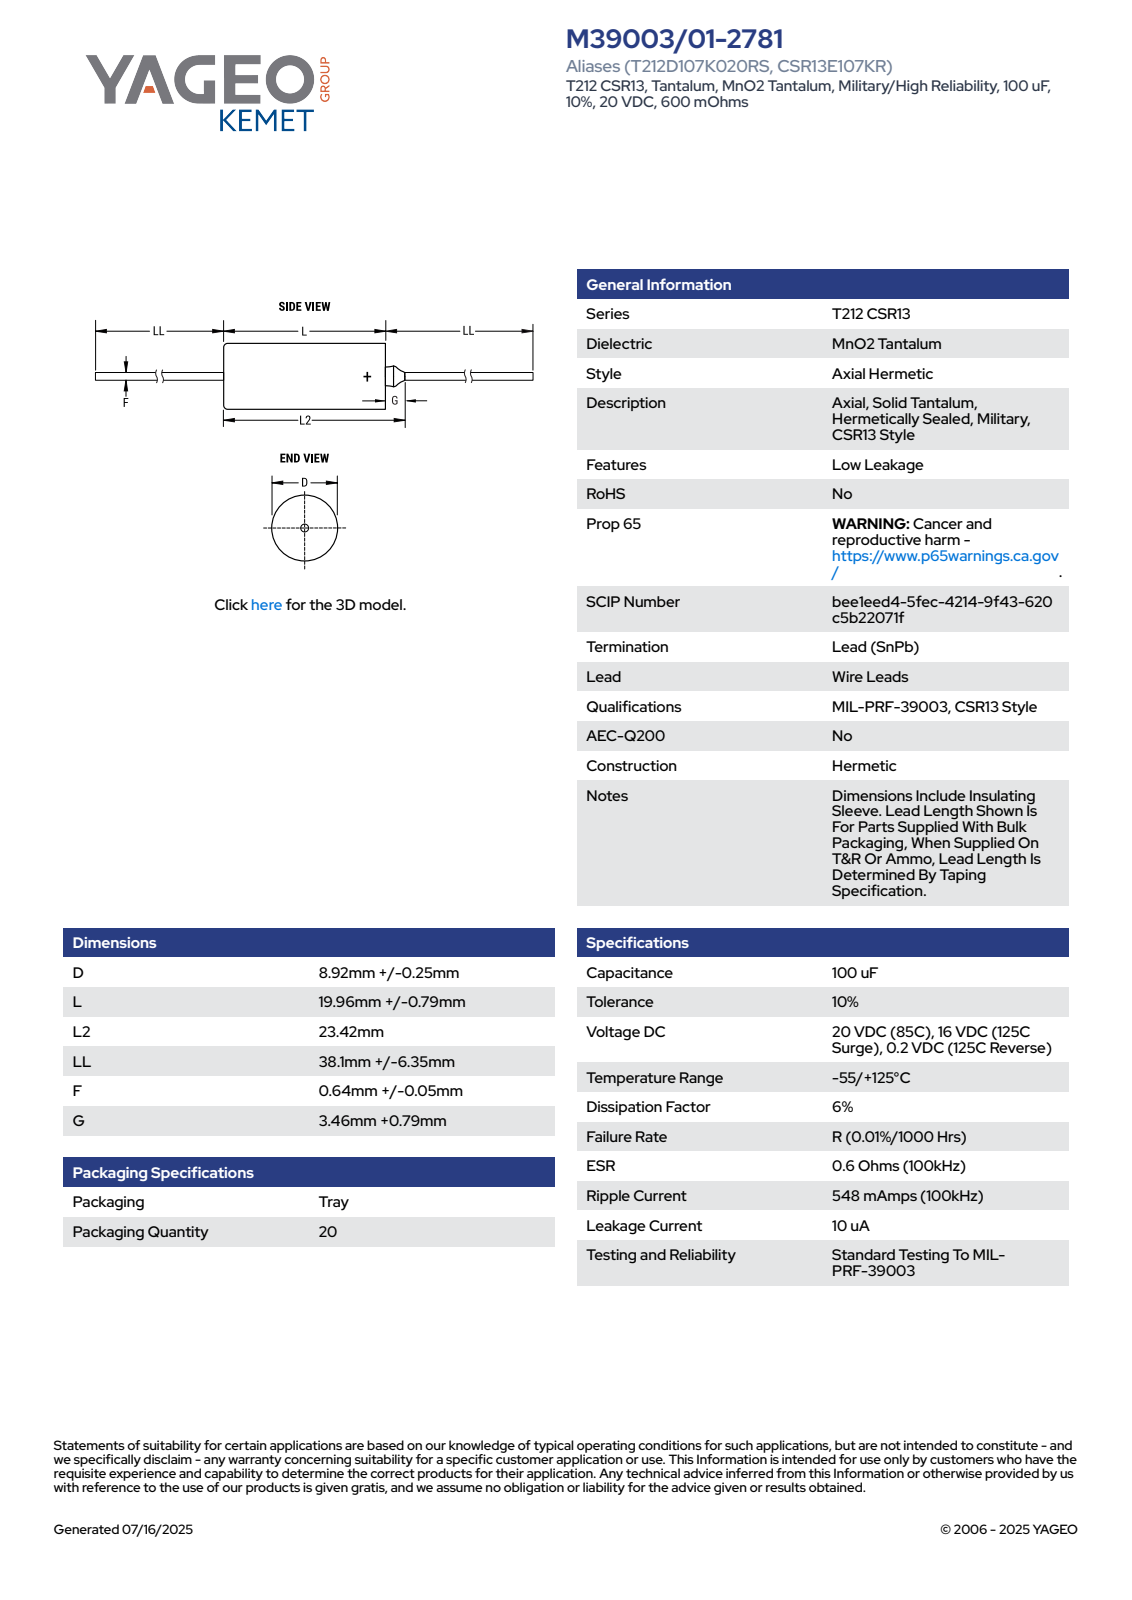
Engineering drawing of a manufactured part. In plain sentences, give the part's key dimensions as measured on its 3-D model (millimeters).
The part is named "CTAM_AHTWG_D9.17L20.75L223.42LL44.45F0.69G4.25". Its 3-D file was written by "SolidWorks 2014 (AUTOMOTIVE_DESIGN)". It is 1 solid with 98 faces: 29 planar, 30 cylindrical and 39 other. Overall it measures 109.65 by 9.17 by 9.17 millimeters. Its volume is 1 091 cubic millimeters and its surface area 1 081 square millimeters. Round holes: 1 of diameter 8.77. Round bosses or shafts: 1 of diameter 9.17, 1 of diameter 1.33, 1 of diameter 1.3, 1 of diameter 0.69. Partial cylindrical surfaces (rounded edges, fillets, slot ends): 1 of radius 4.58. The main face-to-face distances are 15.43, 20.58, 5.15, 44.62, 60.05, 65.2, 109.65, 65.03, 49.6, 44.45.
